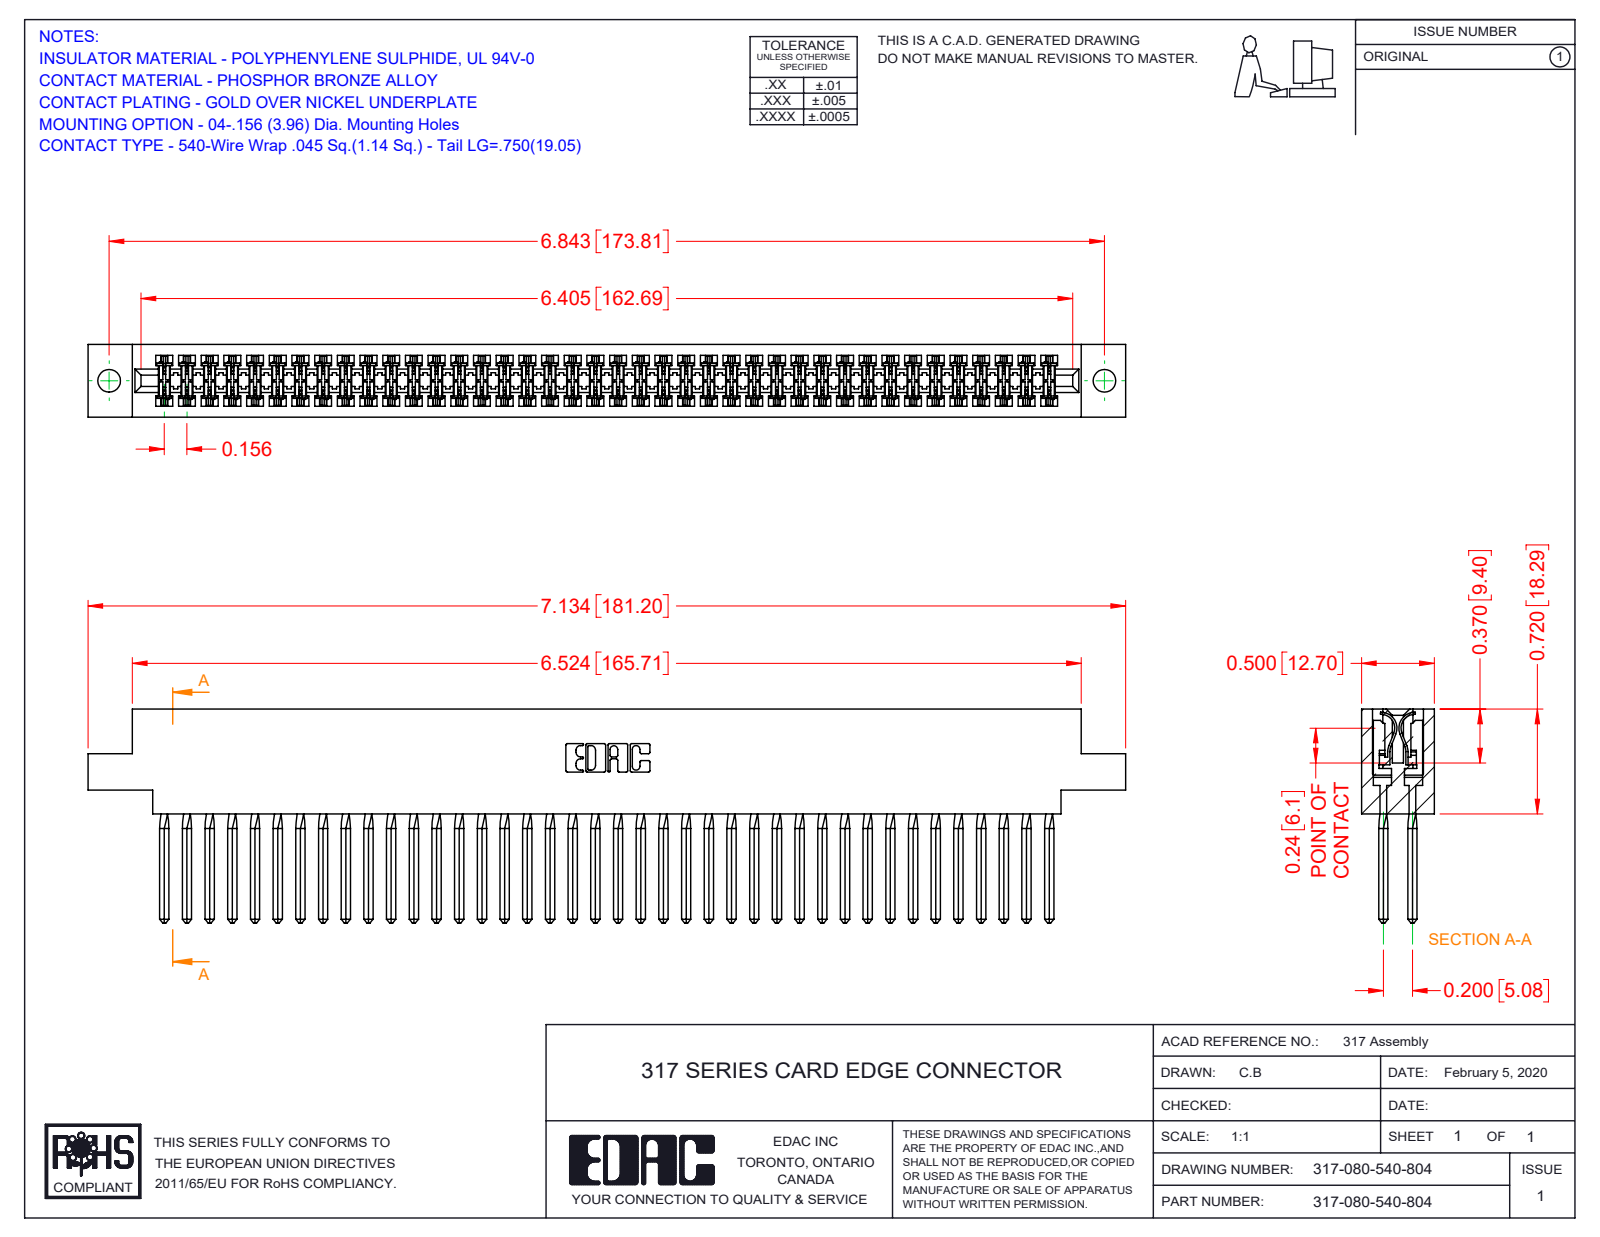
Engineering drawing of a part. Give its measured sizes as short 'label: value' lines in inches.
name: 317-290-001_540; 317 Part_.156 Dia - TH; 317-080-540-804
written by: SolidWorks 2016 (CONFIG_CONTROL_DESIGN)
unit: in
bodies: 81 solids, 7222 faces (5898 planar, 1004 cylindrical, 320 other)
size: 7.134 × 1.47 × 0.5
volume: 1.846 in³; area: 69.53 in²
holes: 2× ⌀0.156
rounds: 160× R0.015, 22× R0.01, 6× R0.007, 6× R0.031, 3× R0.026, 2× R0.095, 2× R0.1, 2× R0.11
face distances: 0.5, 0.075, 0.425, 0.35, 0.195, 0.094, 0.2, 0.115, 0.131, 0.11
hole spacings: 6.843
